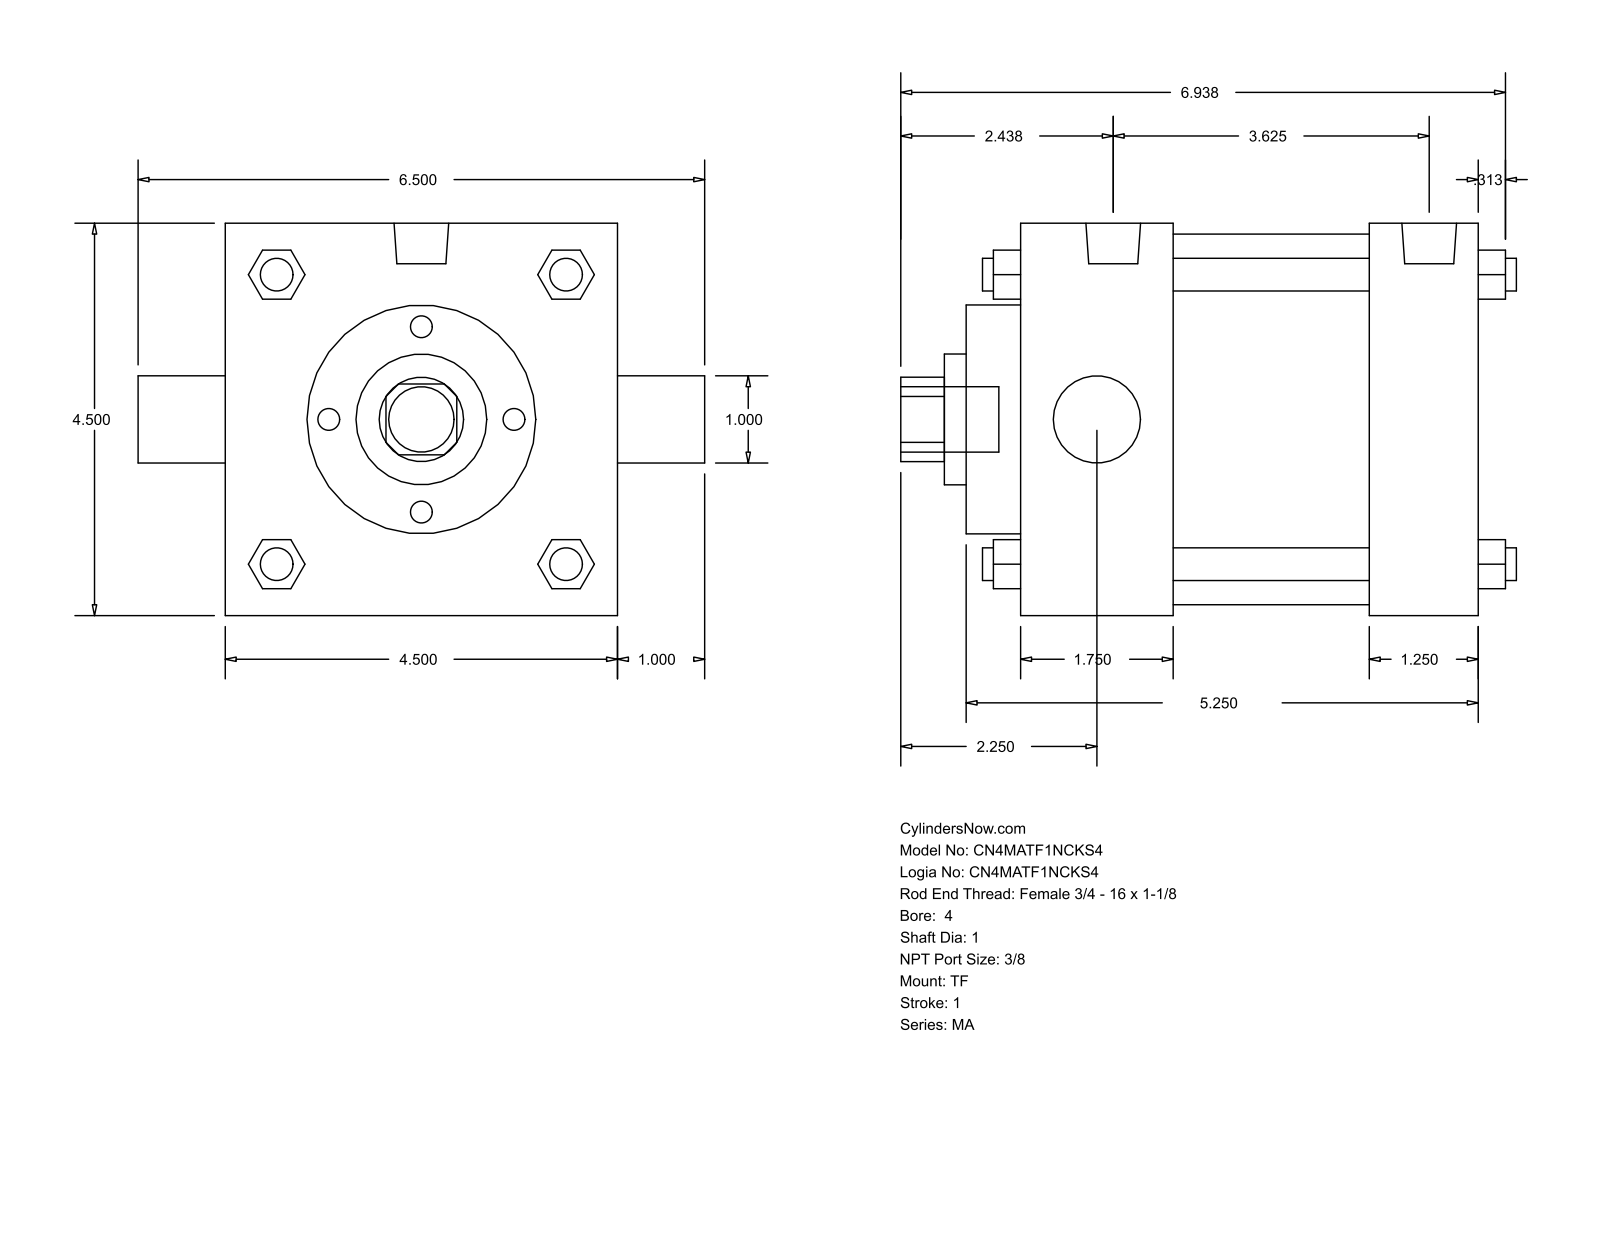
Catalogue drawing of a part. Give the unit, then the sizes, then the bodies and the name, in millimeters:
Units: millimetres
Overall size (bounding box): 179.39 × 165.1 × 114.3
Round holes (diameter × count): ⌀25.4 ×2, ⌀38.1 ×1, ⌀66.67 ×1, ⌀107.95 ×1
Round bosses / shafts (diameter × count): ⌀9.53 ×4, ⌀11.11 ×3, ⌀15.93 ×2, ⌀19.05 ×1
Partial cylindrical surfaces — rounded edges, fillets, slot ends (radius × count): R12.29 ×1
Main face-to-face distances: 114.3, 133.36, 101.61, 31.75, 44.46, 57.15, 88.9, 15.87, 60.33, 117.48
Bodies: 0 solids, 122 faces (93 planar, 29 cylindrical, 0 other)
Part name (STEP PRODUCT): MA_TF__0400_1
STEP written by: GSSL Pune (CONFIG_CONTROL_DESIGN)
